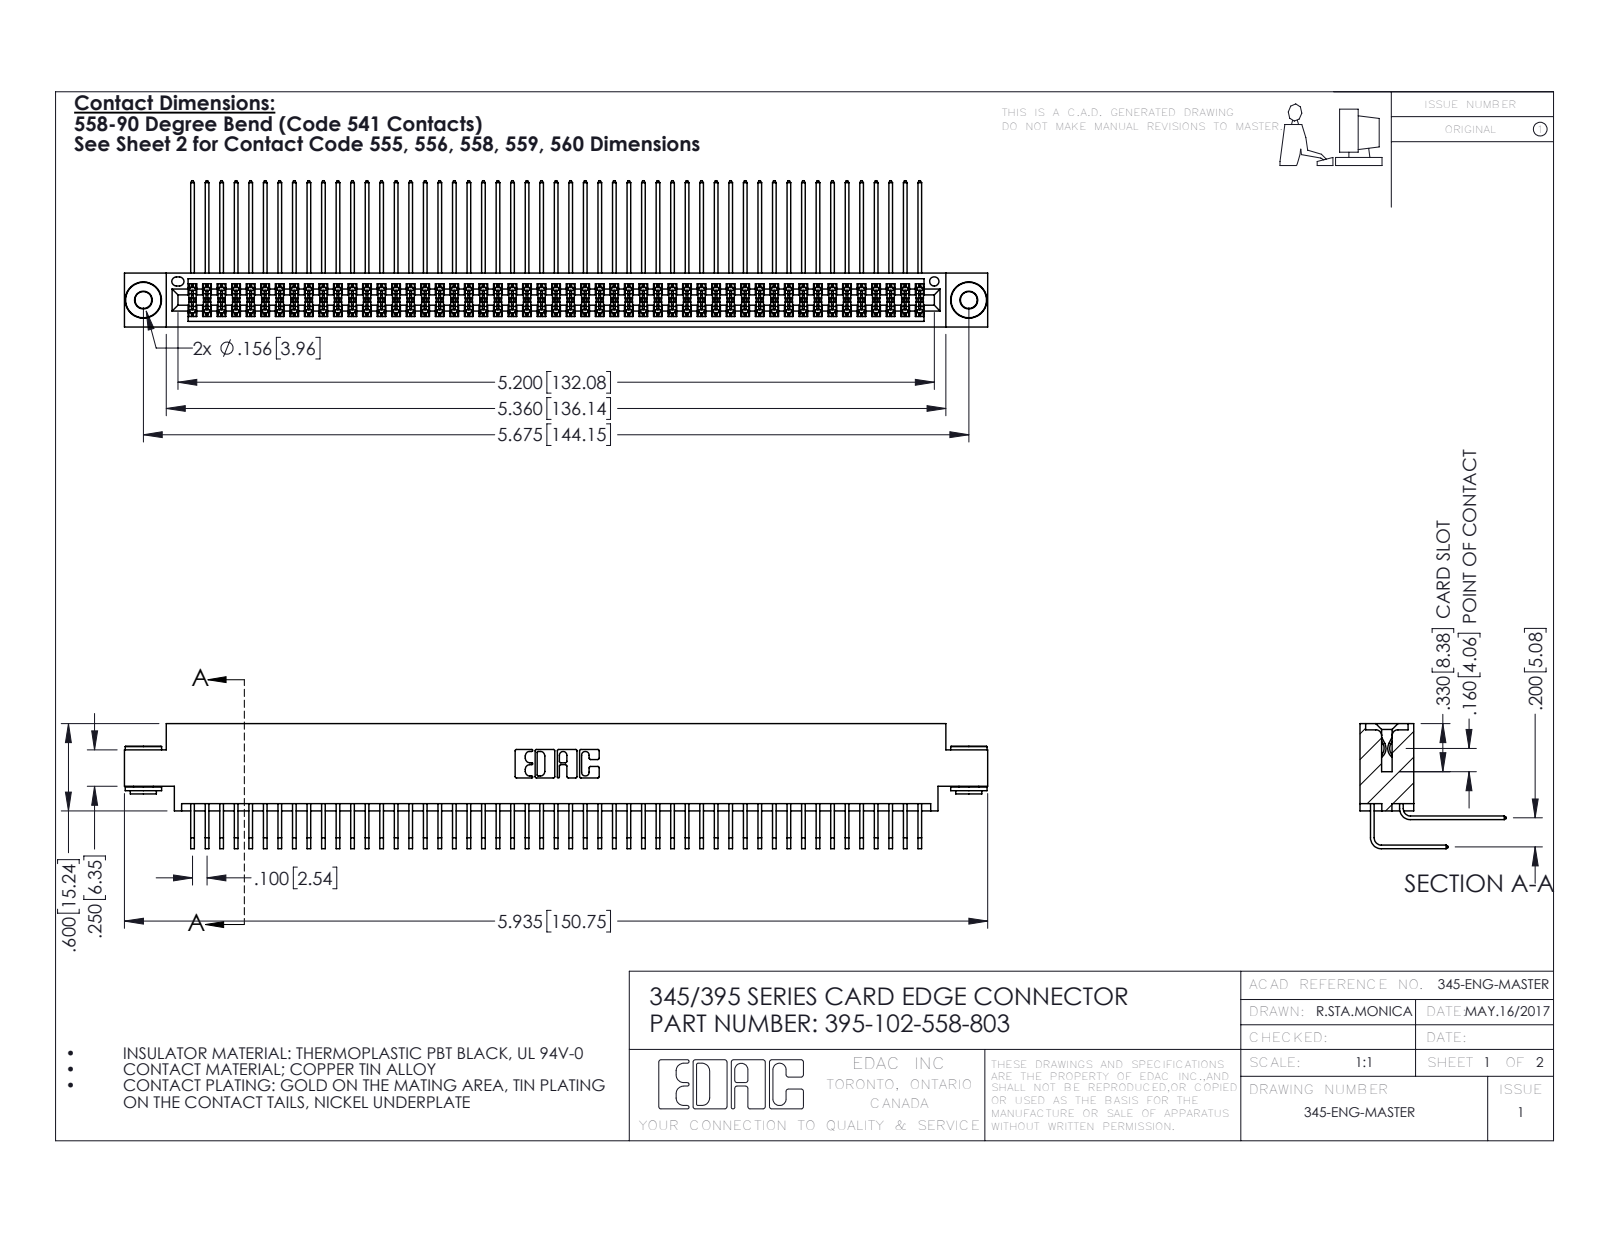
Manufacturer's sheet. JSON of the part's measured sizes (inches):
{"part_name": "345-292-001_558 559 Tail - 1; 345-250-002_345-250-002-102; 395-102-558-803; 345 Part_0.170 Offset - 0.156 Dia-TH (+1 more)", "step_written_by": "SolidWorks 2016 (CONFIG_CONTROL_DESIGN)", "units": "inches", "bodies": {"solids": 105, "faces": 5472, "planar": 3664, "cylindrical": 1800, "other": 8}, "overall_size": [5.935, 1.005, 0.859], "volume_in3": 0.929, "surface_area_in2": 39.97, "round_holes": [[0.116, 2], [0.156, 2], [0.064, 1]], "round_bosses_or_shafts": [[0.25, 2], [0.18, 2], [0.136, 2]], "partial_cylinders_radius": [[0.006, 154], [0.01, 22], [0.007, 6], [0.031, 6], [0.026, 3], [0.014, 2], [0.019, 2], [0.022, 2]], "face_to_face_distances": [0.072, 0.298, 0.2, 0.37, 0.098, 0.272, 0.025, 0.225, 0.175, 0.025], "hole_center_spacings": [0.27, 5.439, 5.675]}
